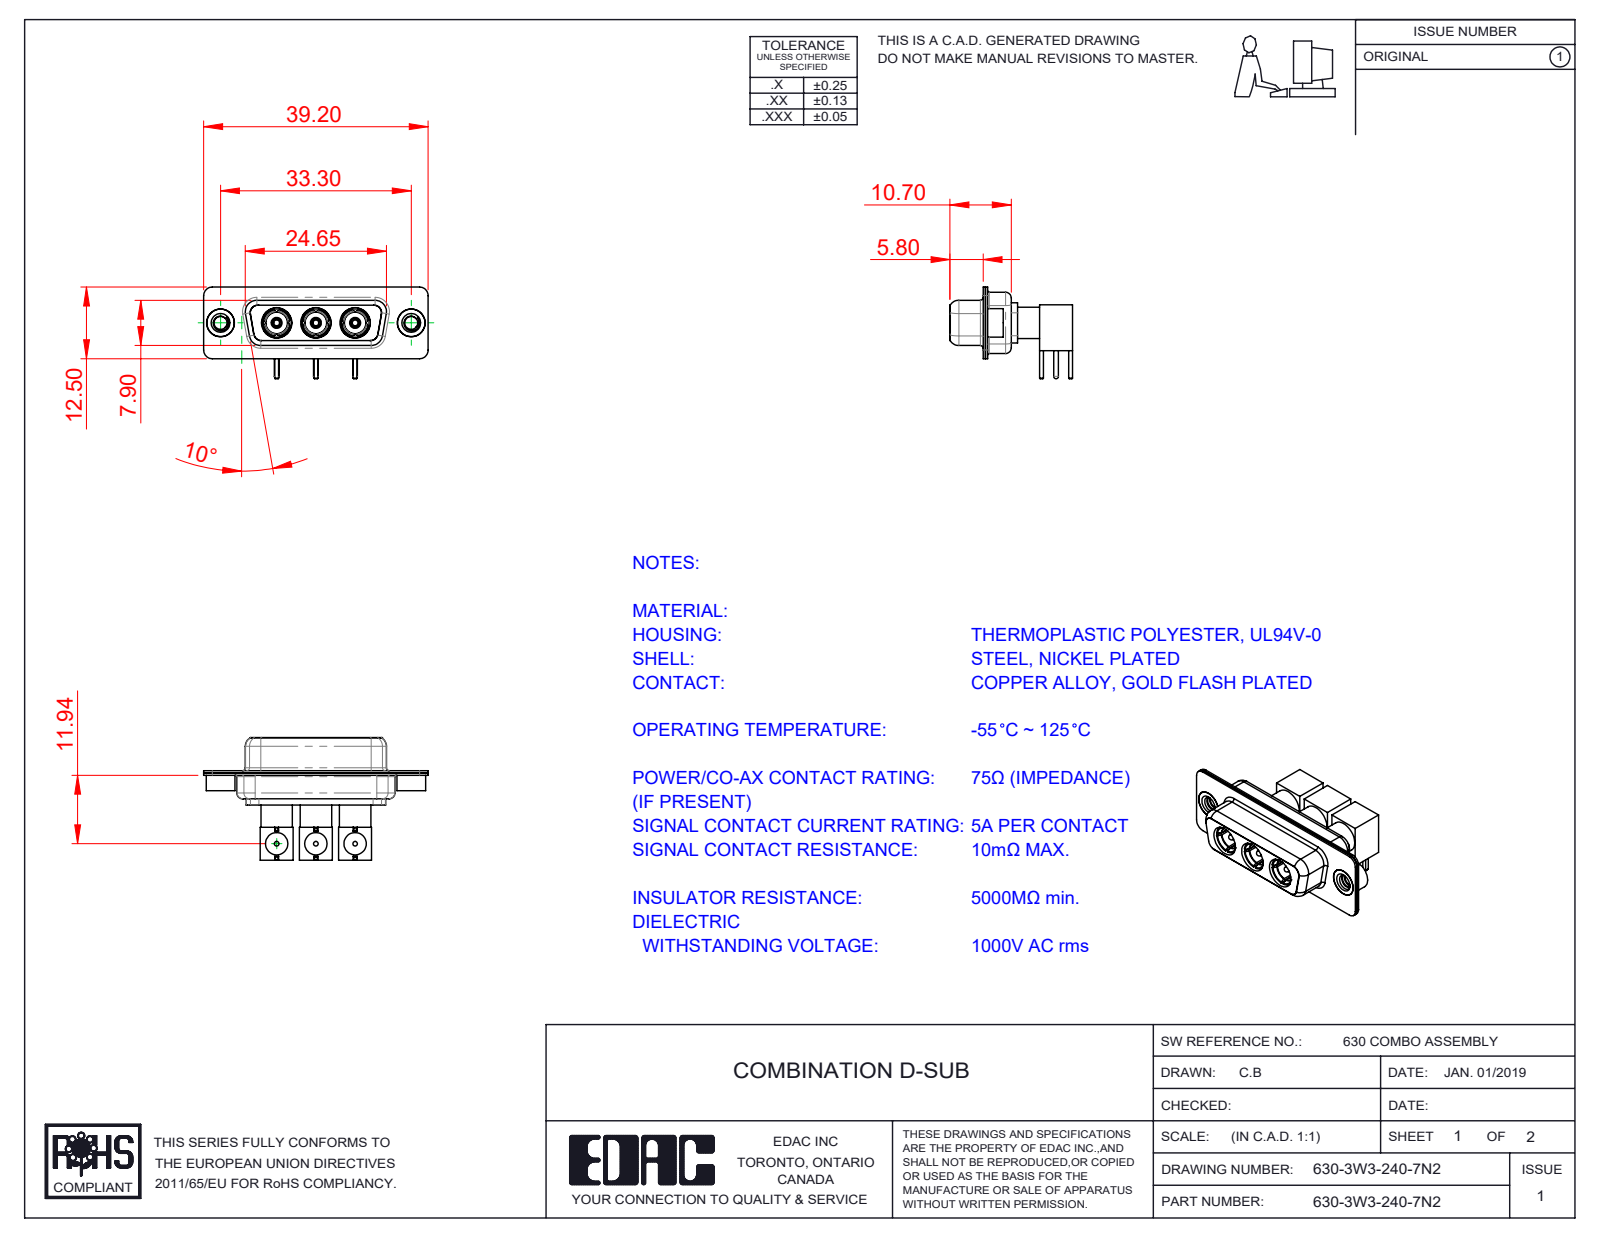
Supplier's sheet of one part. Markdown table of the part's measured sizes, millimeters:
| quantity | value |
| --- | --- |
| part name | Co-Ax Plug Assy_RA; Locking Collar; 630Combo Shell Front_15 Contacts; 630Combo Housing_3W3 (+8 more) |
| STEP written by | SolidWorks 2020 (CONFIG_CONTROL_DESIGN) |
| units | millimeters |
| bodies | 23 solids, 783 faces (268 planar, 332 cylindrical, 183 other) |
| overall size | 39.2 × 21.41 × 16 |
| volume | 3 140 mm³ |
| surface area | 7 790 mm² |
| round holes (diameter × count) | 4.85 × 5, 0.8 × 3, 1.1 × 3, 1.5 × 3, 2.83 × 3, 3.1 × 3, 3.3 × 3, 3.9 × 3, 3.92 × 3, 4.1 × 3, 5.3 × 3, 2.26 × 2 |
| round bosses / shafts (diameter × count) | 5 × 5, 5.5 × 3, 5.2 × 3, 4.75 × 3, 4.15 × 3, 4 × 3, 3.76 × 3, 3.75 × 3 |
| partial cylindrical surfaces (radius × count) | 1.5 × 16, 1.35 × 12, 2 × 12, 1.6 × 8, 0.25 × 4, 0.5 × 4, 0.6 × 4, 0.65 × 4 |
| main face-to-face distances | 0.4, 1.8, 1.4, 0.45, 8.45, 0.8, 8.9, 1.85, 6.85, 6.2 |
| hole center spacings | 6.85, 9.8, 13.7, 16.65, 23.5, 33.3 |
